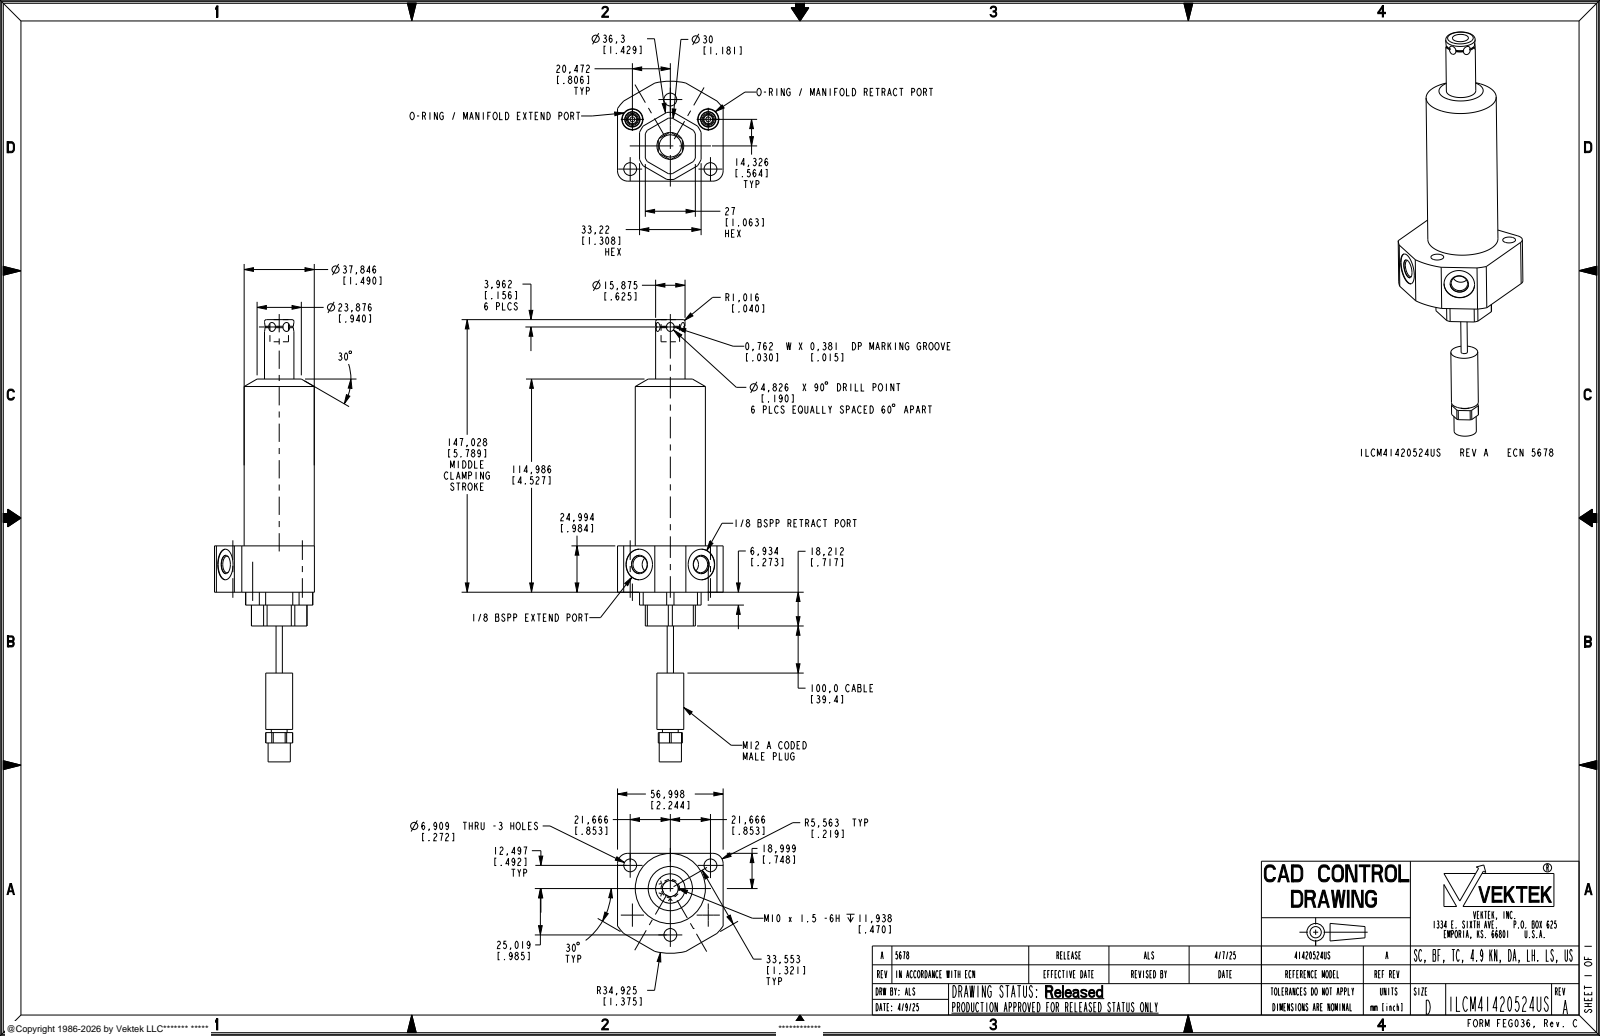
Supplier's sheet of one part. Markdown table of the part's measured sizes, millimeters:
| quantity | value |
| --- | --- |
| part name | ILCM41420524US |
| STEP written by | CREO PARAMETRIC BY PTC INC, 2021164 (AUTOMOTIVE_DESIGN) |
| units | millimeters |
| bodies | 1 solid, 194 faces (79 planar, 81 cylindrical, 34 other) |
| overall size | 238.54 × 69.92 × 65 |
| volume | 190 770 mm³ |
| surface area | 30 668 mm² |
| round holes (diameter × count) | 6.91 × 3, 2.49 × 2, 6.5 × 2, 8.84 × 2, 9.91 × 2, 11.4 × 2, 16.5 × 2, 8.61 × 1 |
| round bosses / shafts (diameter × count) | 5.49 × 2, 37.85 × 1, 15.88 × 1, 14.5 × 1, 11.99 × 1, 10.01 × 1, 8.51 × 1, 3.4 × 1 |
| partial cylindrical surfaces (radius × count) | 5.56 × 2, 7.56 × 1, 15 × 1, 18.15 × 1, 34.92 × 1 |
| main face-to-face distances | 24.99, 57, 18.22, 43.21, 3.11, 30.11, 27, 11.28, 6.94, 31.93 |
| hole center spacings | 25.02, 23.09, 24.99, 26.86, 43.33, 49.96, 40.94, 43.34 |
